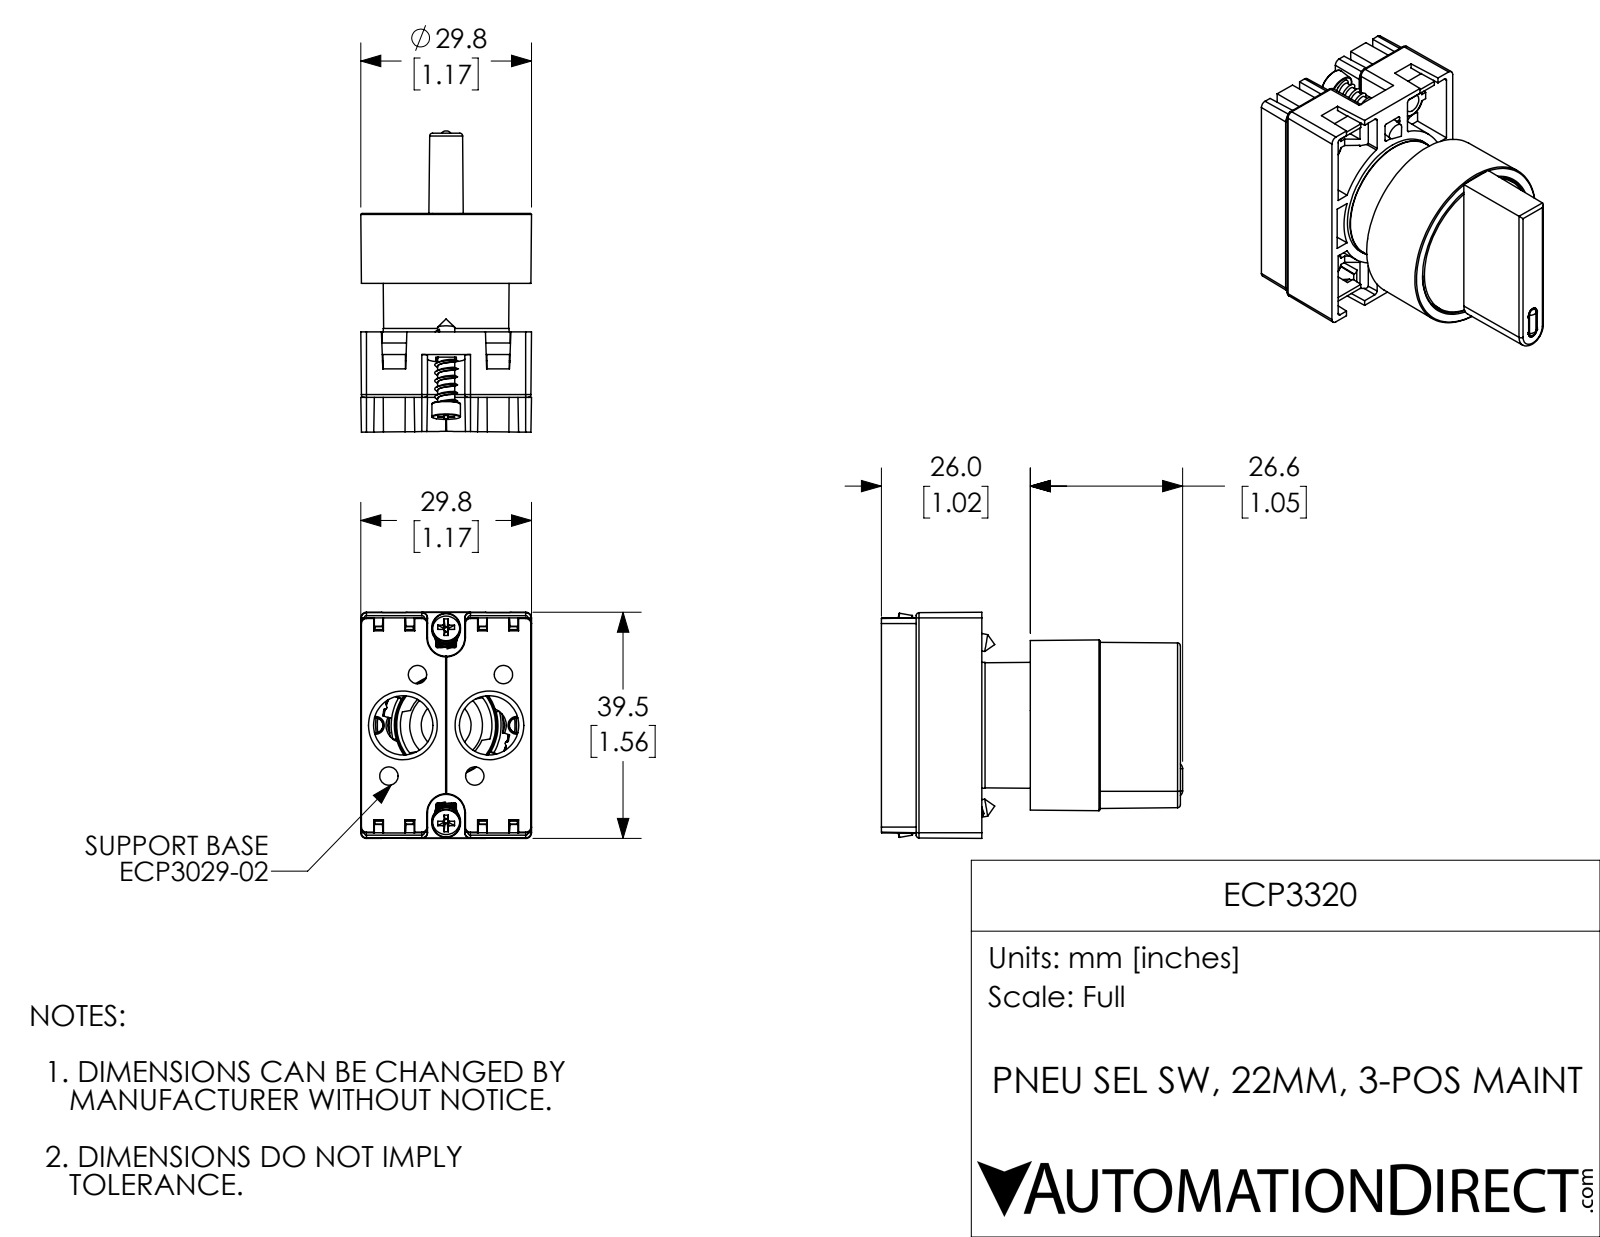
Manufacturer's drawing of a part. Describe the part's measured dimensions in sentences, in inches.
The part is named "ECP3320". Its 3-D file was written by "SolidWorks 2017 (AUTOMOTIVE_DESIGN)". It is 8 solids with 839 faces: 404 planar, 157 cylindrical and 278 other. Overall it measures 2.071 by 1.555 by 1.173 inches. Its volume is 1.095 cubic inches and its surface area 31.53 square inches. Round holes: 4 of diameter 0.081, 2 of diameter 0.407, 1 of diameter 0.5, 1 of diameter 0.551, 1 of diameter 0.697, 1 of diameter 0.75, 1 of diameter 0.756, 1 of diameter 0.854, 1 of diameter 0.976, 1 of diameter 1.024. Round bosses or shafts: 2 of diameter 0.197, 2 of diameter 0.118, 1 of diameter 1.004, 1 of diameter 0.866, 1 of diameter 0.85, 1 of diameter 0.669, 1 of diameter 0.343. Partial cylindrical surfaces (rounded edges, fillets, slot ends): 21 of radius 0.02, 10 of radius 0.012, 9 of radius 0.039, 8 of radius 0.006, 4 of radius 0.008, 2 of radius 0.008, 2 of radius 0.118, 2 of radius 0.128. The main face-to-face distances are 1.265, 0.059, 0.067, 0.712, 0.743, 0.299, 0.712, 0.715, 0.814, 0.451. The hole center spacings are 0.304, 0.541, 0.817, 0.295, 0.472, 0.972, 1.081, 0.591.
